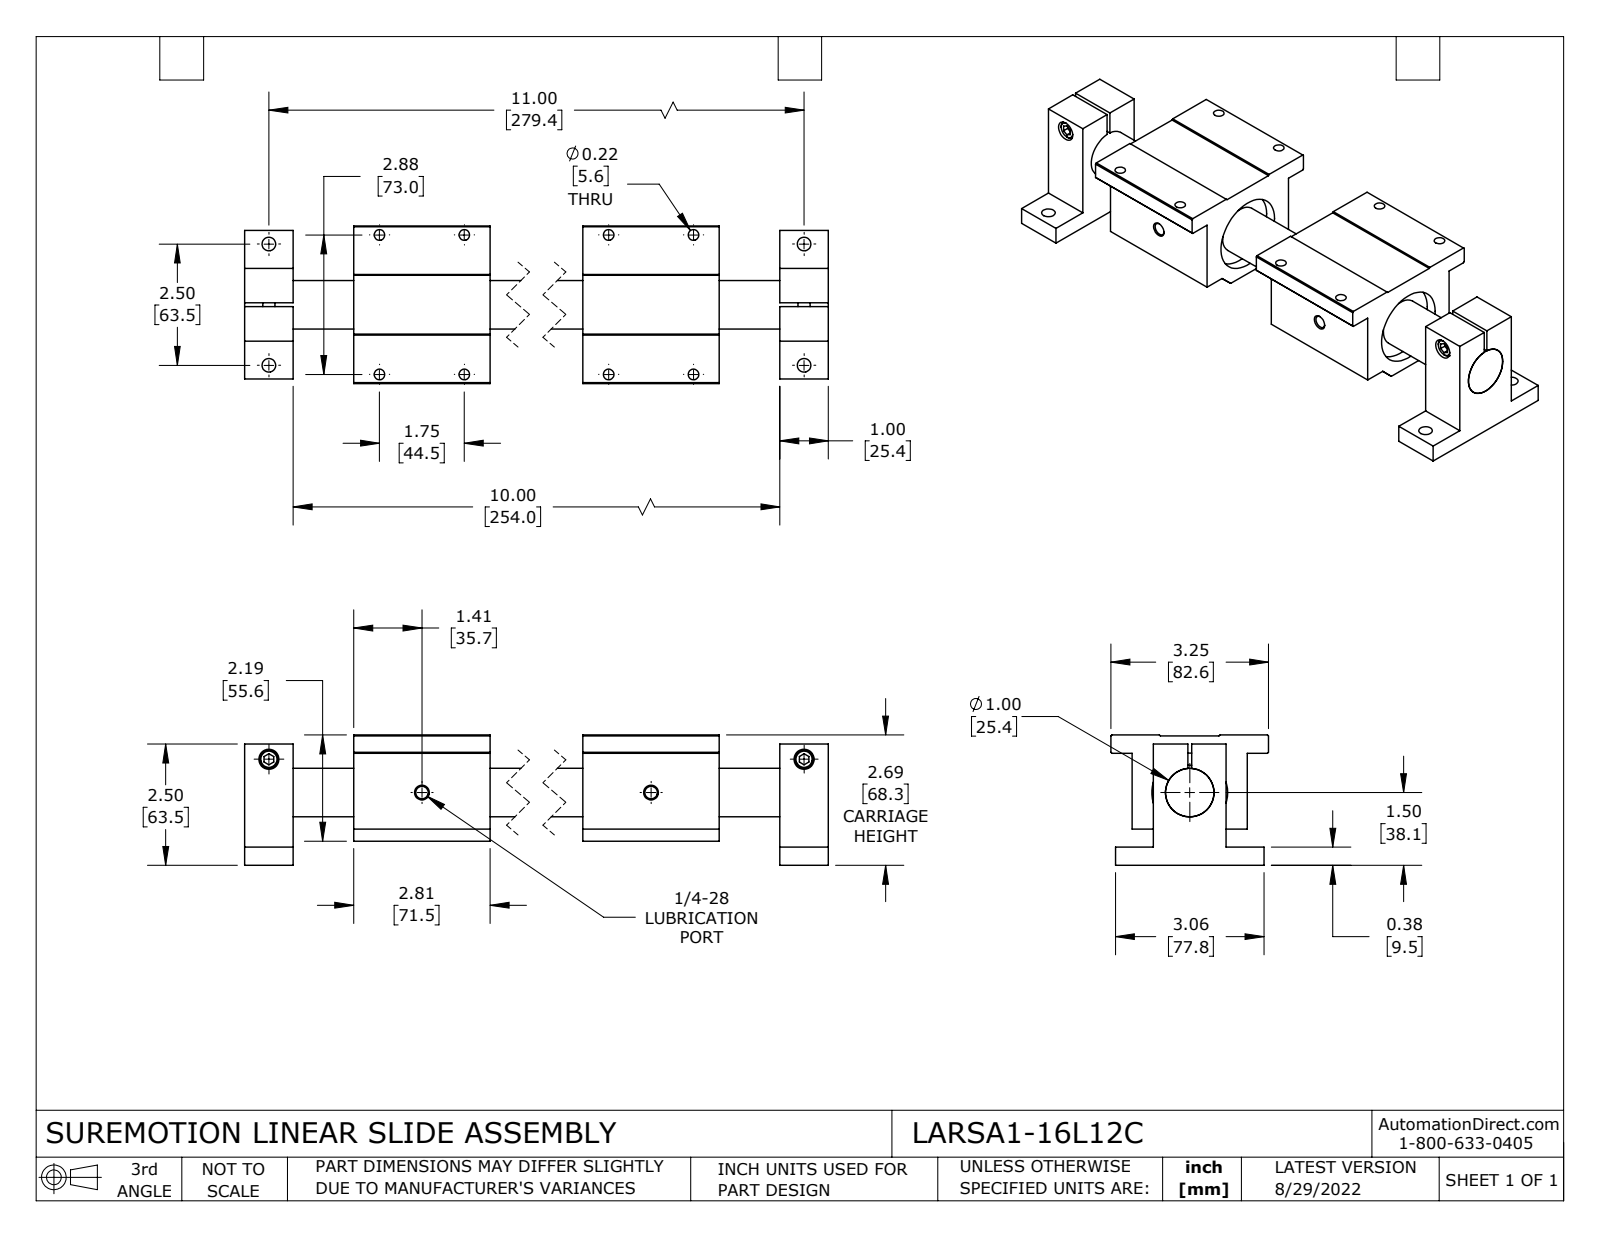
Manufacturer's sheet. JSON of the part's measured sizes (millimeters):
{"part_name": "LARSACC-003; LARSA1-16L12C; LARSA1-16L12C-RAIL", "step_written_by": "SolidWorks 2021 (CONFIG_CONTROL_DESIGN)", "units": "millimeters", "bodies": {"solids": 7, "faces": 166, "planar": 98, "cylindrical": 60, "other": 8}, "overall_size": [304.8, 82.6, 68.2], "volume_mm3": 656600, "surface_area_mm2": 119200, "round_holes": [[5.6, 8], [7.1, 4], [6.6, 2], [10.5, 2], [25.4, 1], [39.7, 1]], "round_bosses_or_shafts": [[9.5, 2], [6.4, 2]], "face_to_face_distances": [71.5, 119, 60.4, 11.1, 49.2, 9.5, 58.7, 279.4, 25.4, 0.5], "hole_center_spacings": [119, 44.5, 58.1, 73, 85.5, 89.5, 102.5, 123.1]}
